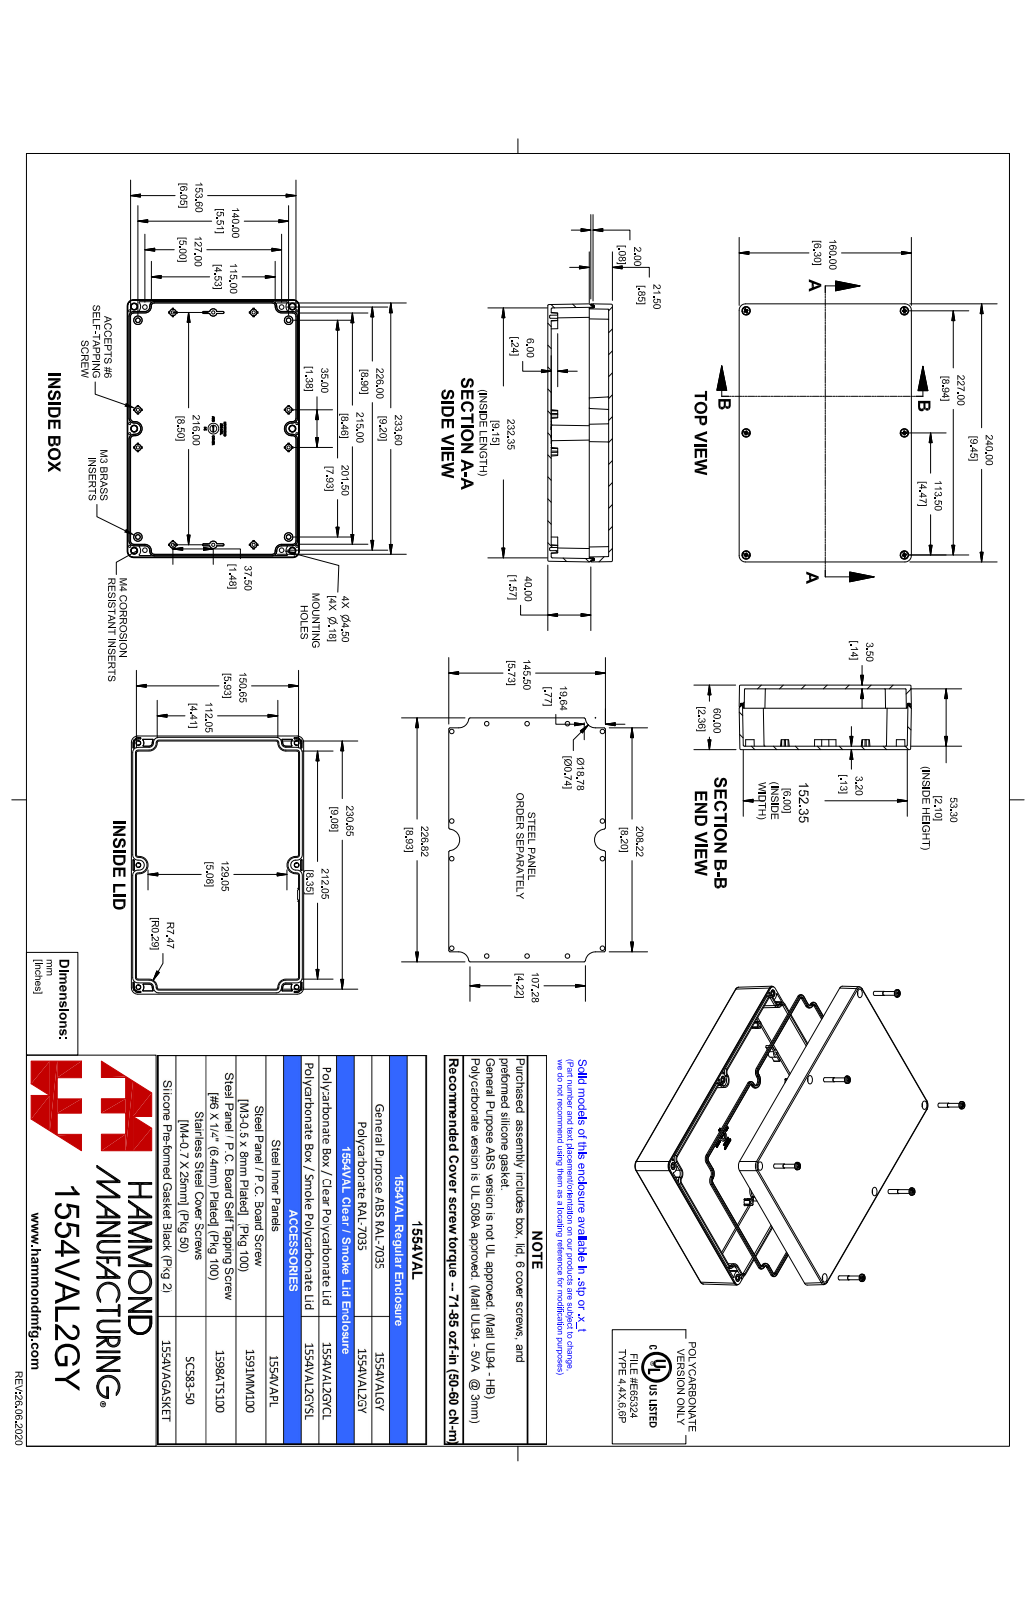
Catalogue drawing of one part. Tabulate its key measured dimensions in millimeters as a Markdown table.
| quantity | value |
| --- | --- |
| part name | 1554VAL2GY |
| STEP written by | SolidWorks 2021 (AUTOMOTIVE_DESIGN) |
| units | millimeters |
| bodies | 19 solids, 2046 faces (692 planar, 434 cylindrical, 920 other) |
| overall size | 240 × 160 × 60 |
| volume | 435 900 mm³ |
| surface area | 279 200 mm² |
| round holes (diameter × count) | 3.3 × 6, 2.5 × 4, 4.6 × 4 |
| round bosses / shafts (diameter × count) | 6.9 × 6, 6.4 × 6, 5.5 × 6, 5.3 × 6, 3.9 × 6, 3.5 × 6, 4.8 × 4, 3.9 × 4 |
| partial cylindrical surfaces (radius × count) | 0.5 × 33, 0.3 × 28, 1 × 24, 2.5 × 12, 5 × 12, 6 × 8, 0.8 × 6, 1.5 × 4 |
| main face-to-face distances | 3.2, 60, 3.5, 56.5, 53.3, 56.8, 4.7, 160, 156.8, 155.3 |
| hole center spacings | 13.2, 100.8, 113.5, 144.1, 175.3, 185.7, 214.3, 257.9 |
